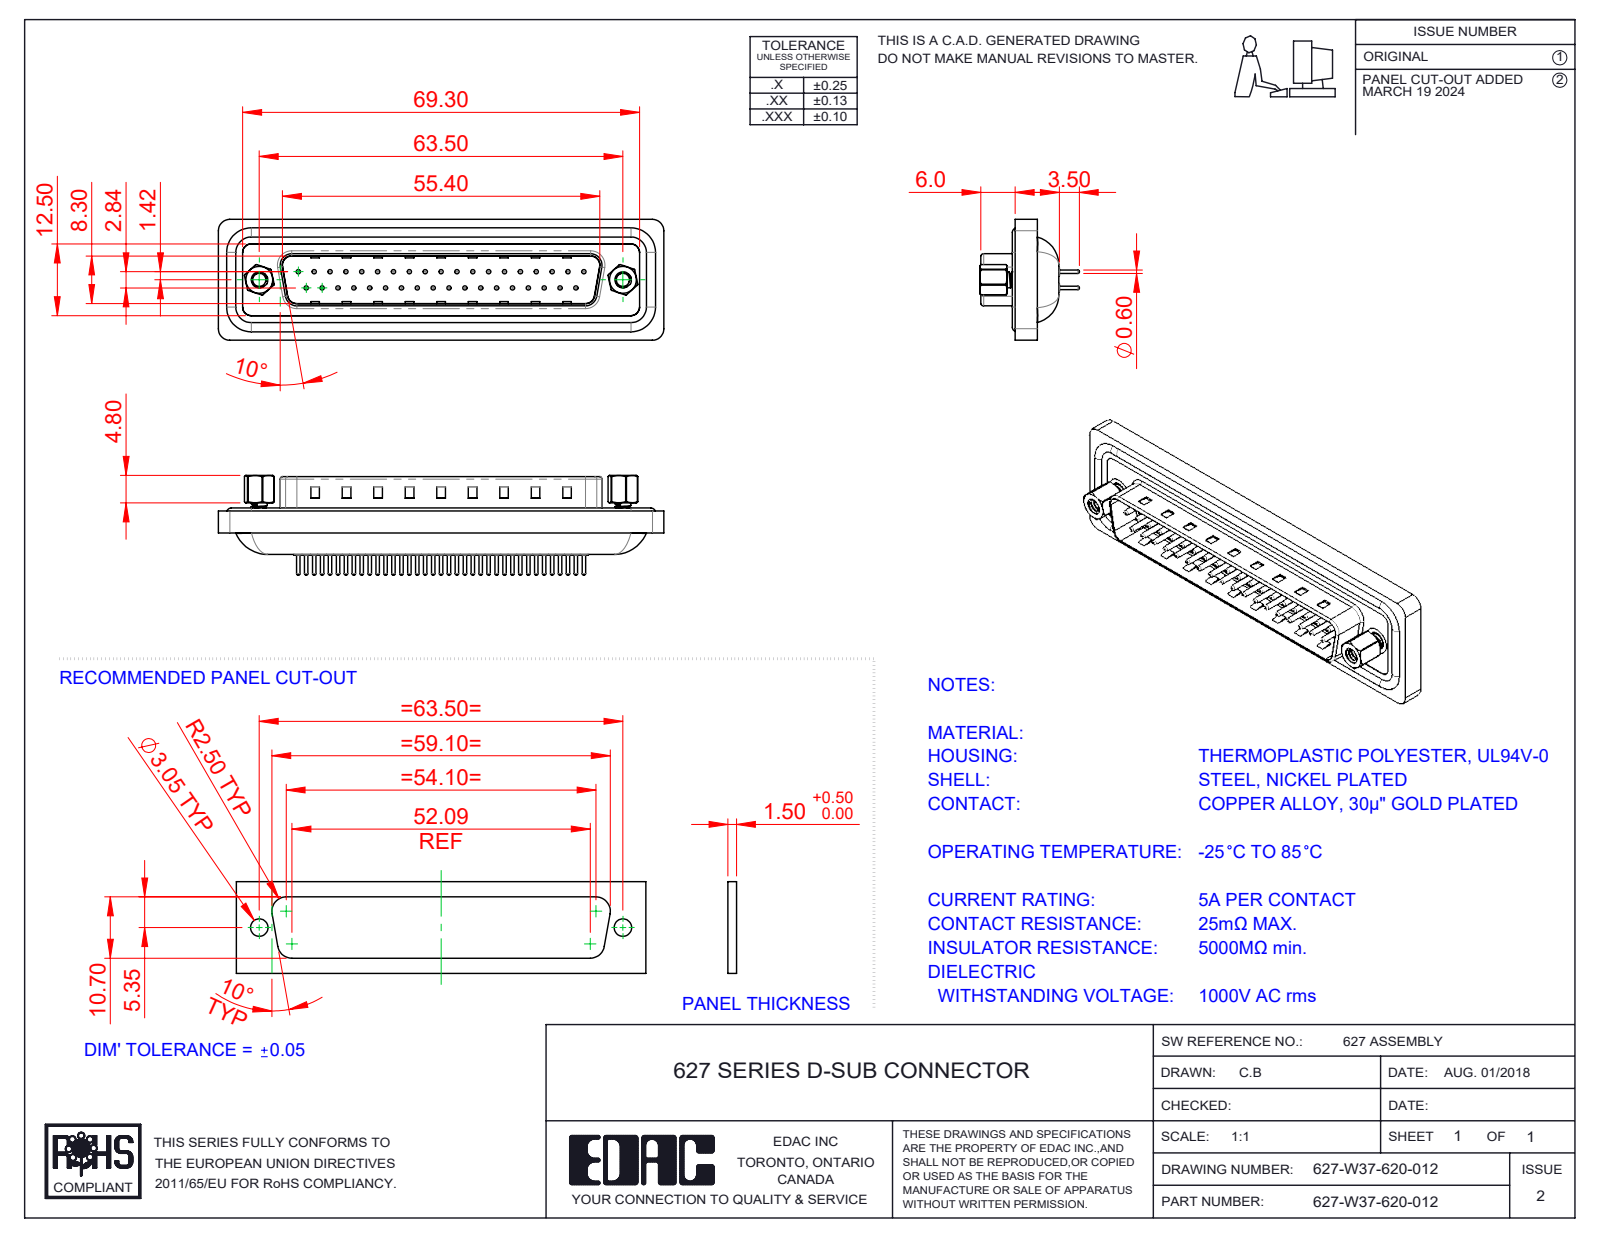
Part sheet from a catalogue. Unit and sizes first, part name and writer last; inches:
Units: inches
Overall size (bounding box): 3.063 × 0.831 × 0.685
Round holes (diameter × count): ⌀0.03 ×37, ⌀0.059 ×37, ⌀0.063 ×37, ⌀0.079 ×37, ⌀0.089 ×2, ⌀0.09 ×2, ⌀0.157 ×2, ⌀0.189 ×2, ⌀0.197 ×2
Round bosses / shafts (diameter × count): ⌀0.024 ×37, ⌀0.059 ×9, ⌀0.063 ×4, ⌀0.193 ×2, ⌀0.11 ×2
Partial cylindrical surfaces — rounded edges, fillets, slot ends (radius × count): R0.079 ×16, R0.059 ×14, R0.02 ×8, R0.106 ×6, R0.035 ×4, R0.063 ×4, R0.169 ×4, R0.016 ×2
Main face-to-face distances: 0.03, 0.016, 0.161, 0.043, 0.108, 0.181, 0.148, 0.222, 0.608, 0.579
Hole centre spacings: 0.124, 0.109, 0.218, 0.327, 0.198, 0.398, 0.436, 0.503
Volume: 0.583 in³ · Surface area: 22.29 in²
Bodies: 45 solids, 1999 faces (496 planar, 816 cylindrical, 687 other)
Part name (STEP PRODUCT): 627W Housing_37 Contacts; 627W 4-40 Hex Standoff; 627W Contact Row 1_20; 627W Waterproof Housing_37 Contacts (+4 more)
STEP written by: SolidWorks 2023 (CONFIG_CONTROL_DESIGN)
